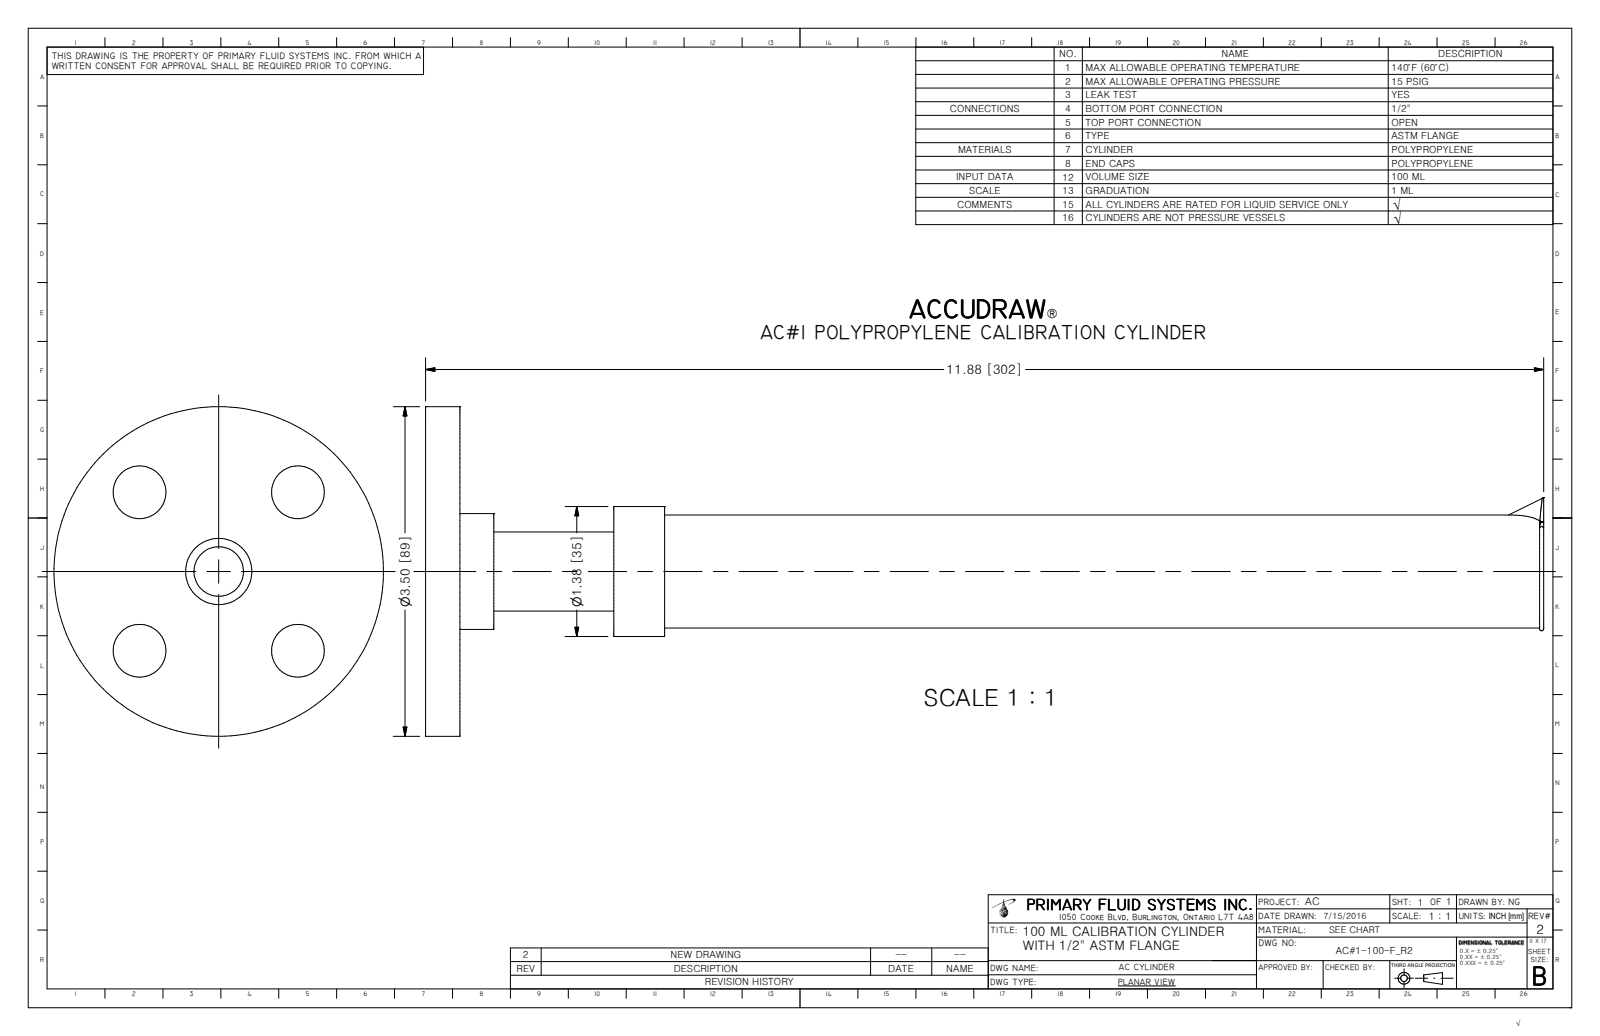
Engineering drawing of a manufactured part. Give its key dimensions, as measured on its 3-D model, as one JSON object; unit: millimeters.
{"part_name": "AC#1-100-F_R2; SA-50FLG-PP_R0; FLG-50PP_R0; PIPE-50PP-SCH80 (+2 more)", "step_written_by": "Autodesk Inventor 2009 (AUTOMOTIVE_DESIGN)", "units": "millimeters", "bodies": {"solids": 4, "faces": 40, "planar": 17, "cylindrical": 15, "other": 8}, "overall_size": [301.7, 88.9, 88.9], "volume_mm3": 100200, "surface_area_mm2": 72970, "round_holes": [[14.2, 4], [13.4, 1], [17.5, 1], [17.9, 1], [21.3, 1], [28.3, 1]], "round_bosses_or_shafts": [[88.9, 1], [35.1, 1], [31.2, 1], [30.5, 1], [25.7, 1]], "face_to_face_distances": [9.3, 50.8, 41.5, 64.5, 55.2, 13.7, 18.4, 9.1, 32.4, 46.1], "hole_center_spacings": [30.2, 42.7, 60.5]}
